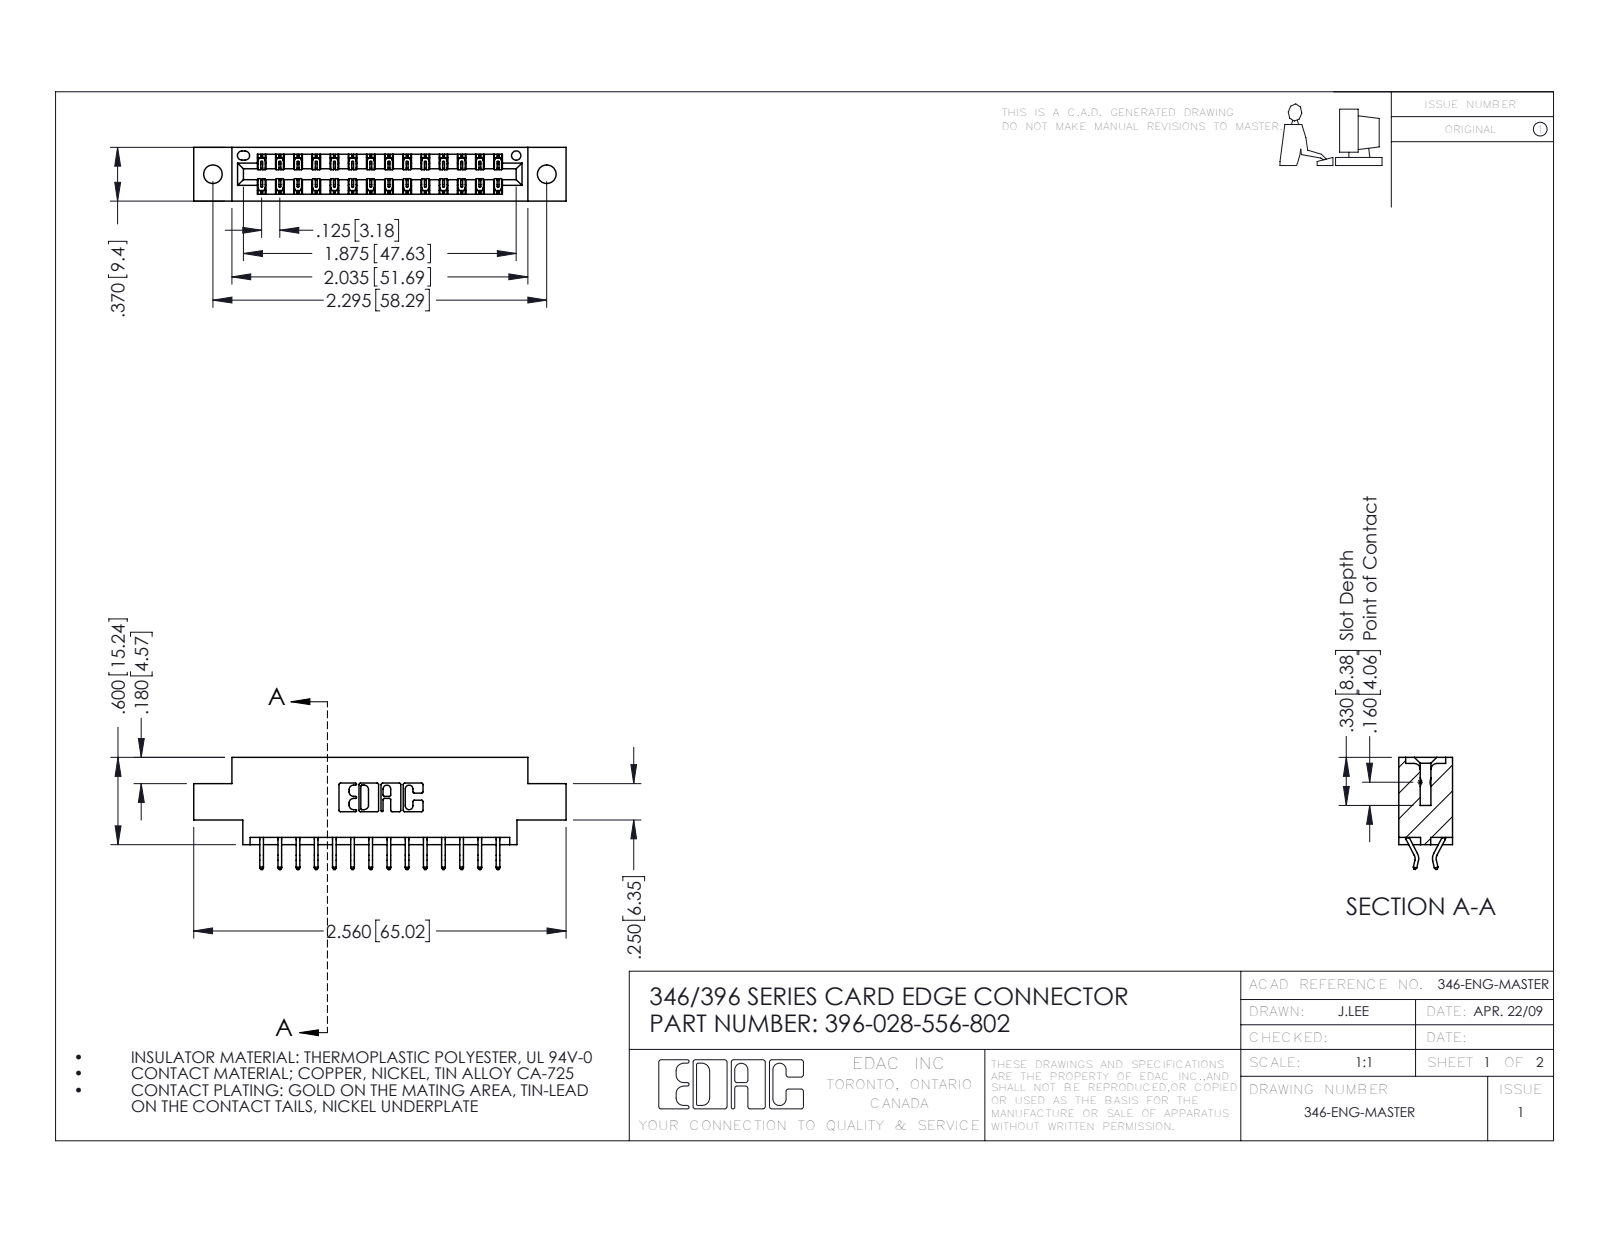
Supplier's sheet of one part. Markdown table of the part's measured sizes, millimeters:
| quantity | value |
| --- | --- |
| part name | 345-292-001_556 Tail; 396-028-556-802; 346 Part_0.170 Offset - 0.128 Dia |
| STEP written by | SolidWorks 2016 (CONFIG_CONTROL_DESIGN) |
| units | millimeters |
| bodies | 29 solids, 1750 faces (1172 planar, 578 cylindrical, 0 other) |
| overall size | 65 × 19.6 × 9.4 |
| volume | 5 930 mm³ |
| surface area | 7 594 mm² |
| round holes (diameter × count) | 3.3 × 2, 1.6 × 1 |
| partial cylindrical surfaces (radius × count) | 0.2 × 42, 0.3 × 22, 0.2 × 6, 0.8 × 6, 0.7 × 3, 0.3 × 2, 0.4 × 2, 0.6 × 2 |
| main face-to-face distances | 1.2, 8.2, 9.4, 6.4, 0.6, 1.8, 7.6, 7, 3.8, 5.6 |
| hole center spacings | 6.2, 53.1, 58.3 |
